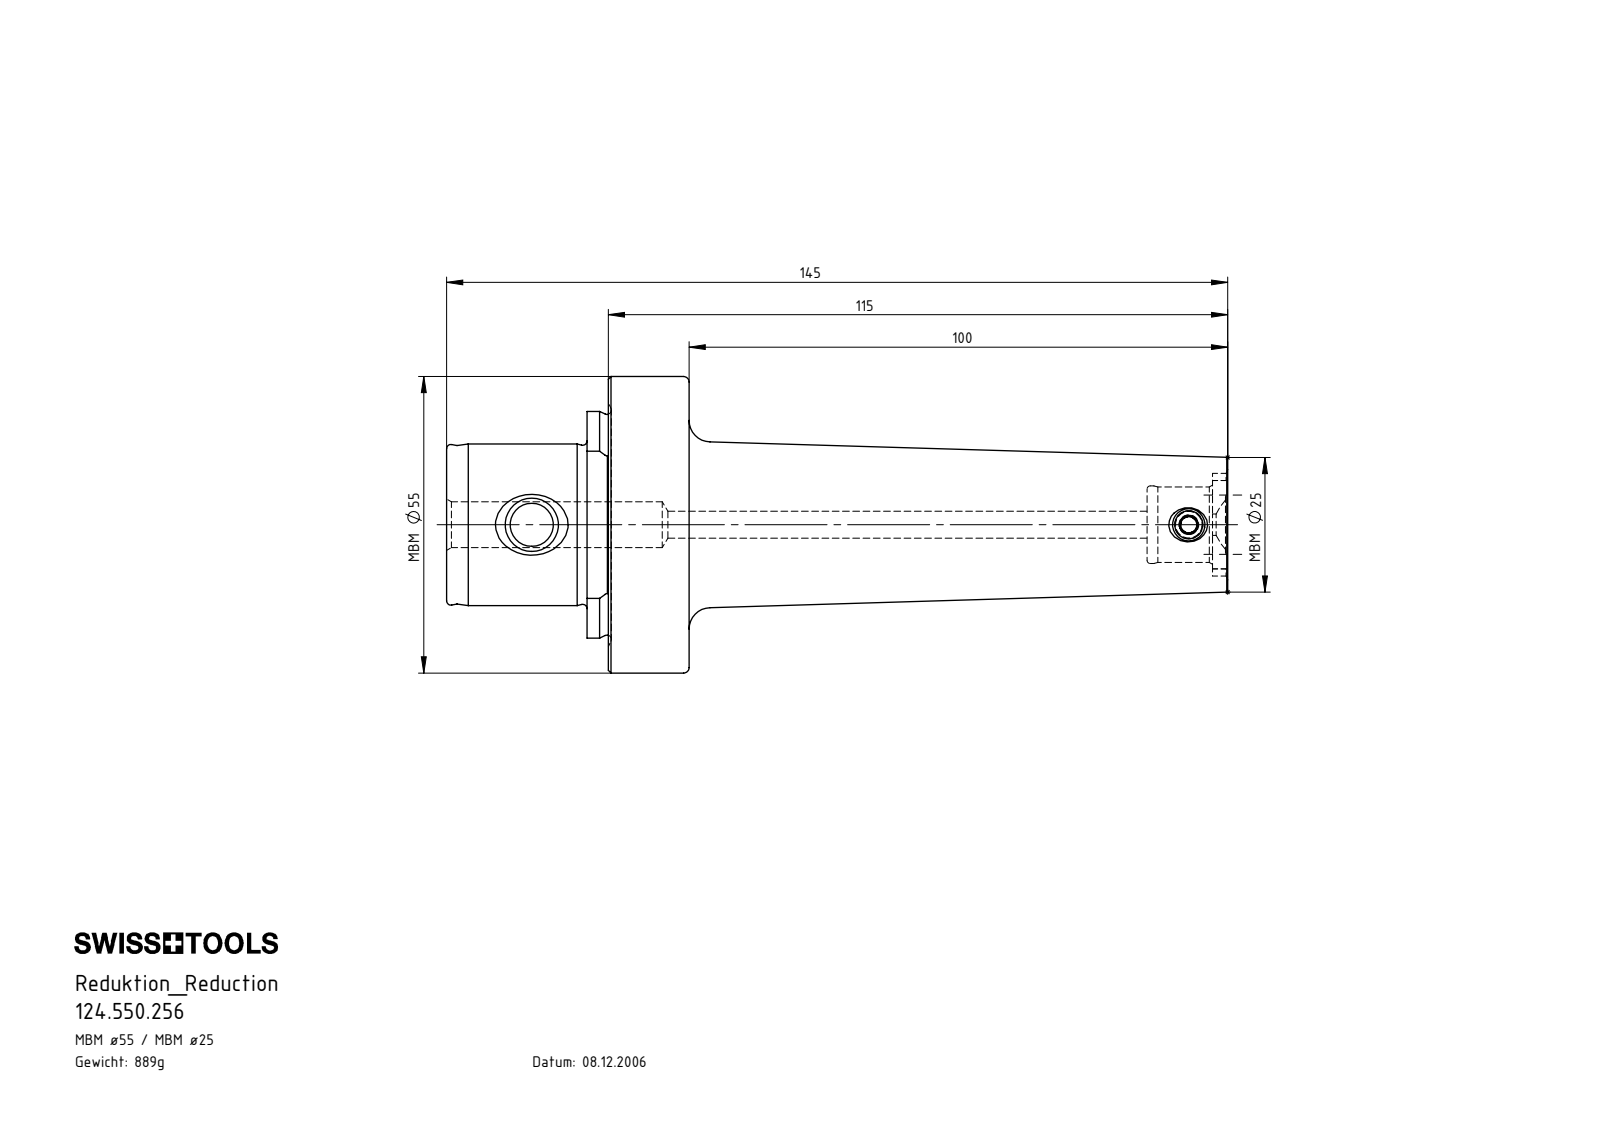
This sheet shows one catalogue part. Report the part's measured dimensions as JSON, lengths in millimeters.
{"part_name": "124.550.256; MB5-MB1.K01.135_C; MB1-ER1.001.006_A", "step_written_by": "SolidWorks 2017 (CONFIG_CONTROL_DESIGN)", "units": "millimeters", "bodies": {"solids": 2, "faces": 139, "planar": 31, "cylindrical": 34, "other": 74}, "overall_size": [165, 55, 55], "volume_mm3": 98356, "surface_area_mm2": 21497, "round_holes": [[2.5, 1], [4.2, 1], [4.5, 1], [8, 1], [8.5, 1], [11, 1], [11.4, 1]], "round_bosses_or_shafts": [[55, 1], [30, 1], [5, 1]], "partial_cylinders_radius": [[2.2, 4], [6.5, 1], [8.03, 1], [21.02, 1]], "face_to_face_distances": [15, 30, 45, 26.05, 3.95, 18.95, 29.85, 3.8, 15.15, 32], "hole_center_spacings": [143.5]}
